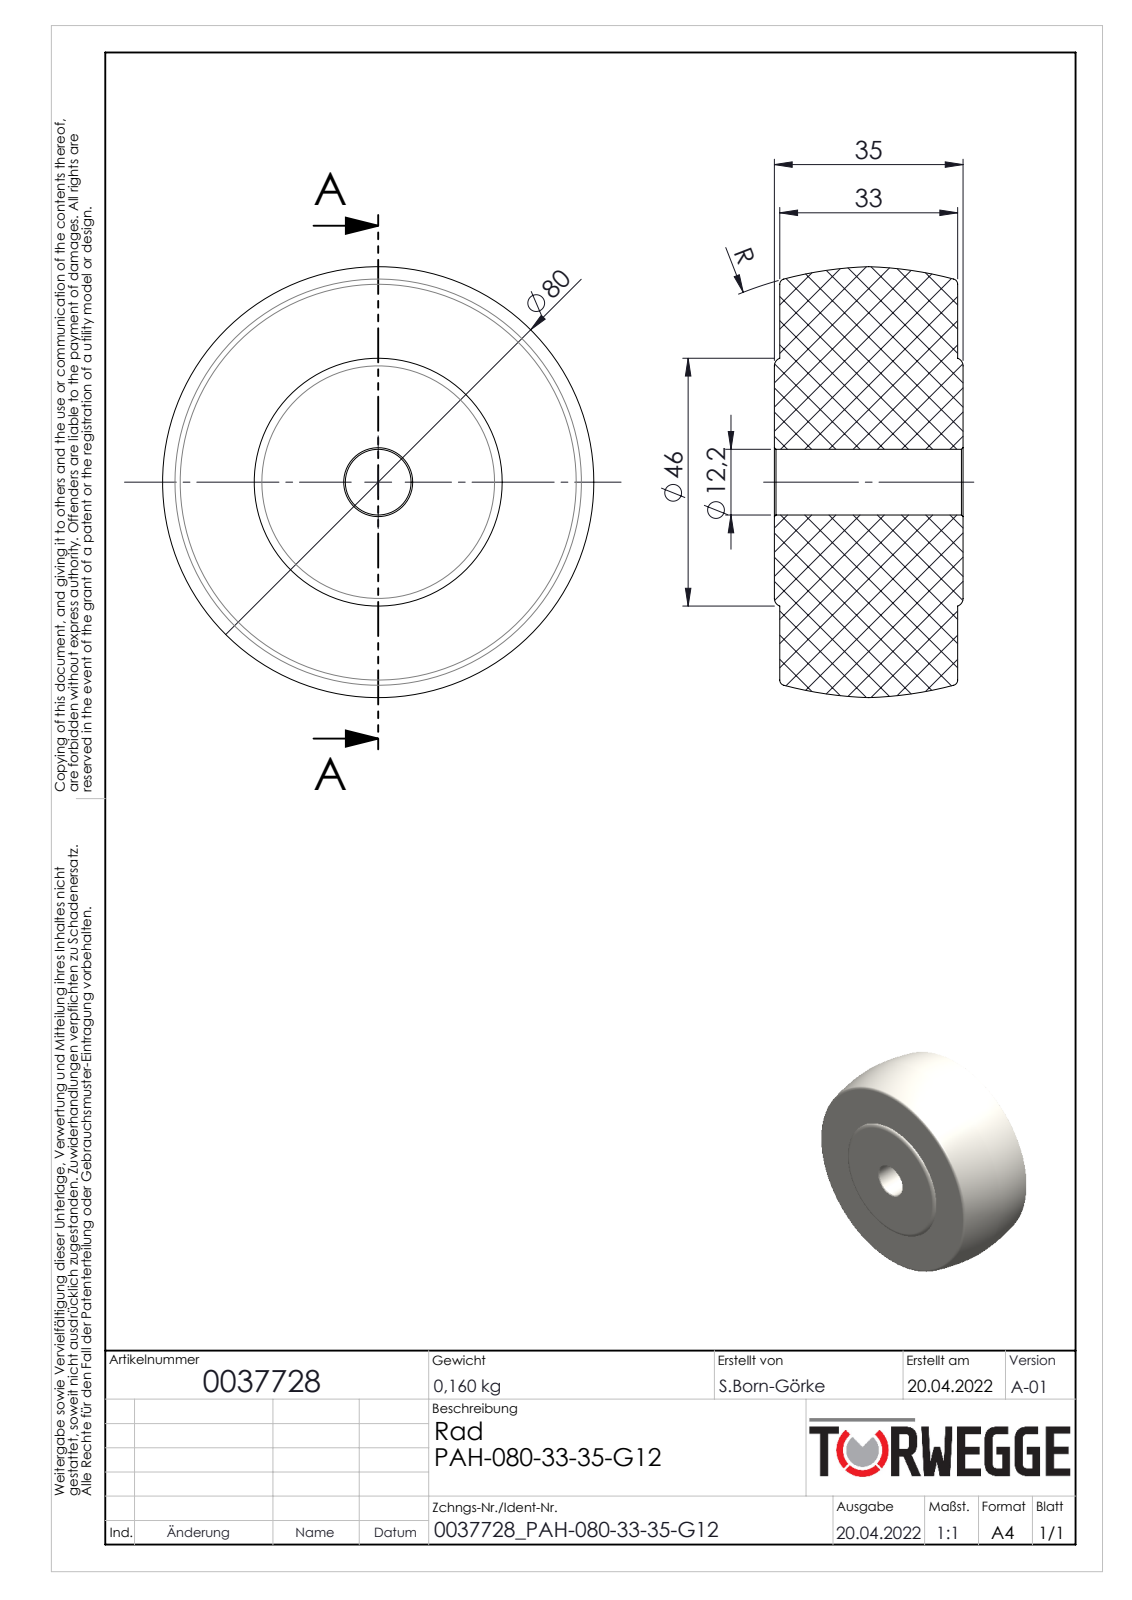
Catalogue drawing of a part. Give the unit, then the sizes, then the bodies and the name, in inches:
Units: inches
Overall size (bounding box): 3.15 × 3.15 × 1.378
Round holes (diameter × count): ⌀0.48 ×1
Main face-to-face distances: 0.039, 1.339, 1.299, 1.378
Volume: 9.612 in³ · Surface area: 28.15 in²
Bodies: 1 solid, 22 faces (4 planar, 2 cylindrical, 16 other)
Part name (STEP PRODUCT): 0037728
STEP written by: SolidWorks 2020 (AUTOMOTIVE_DESIGN)
